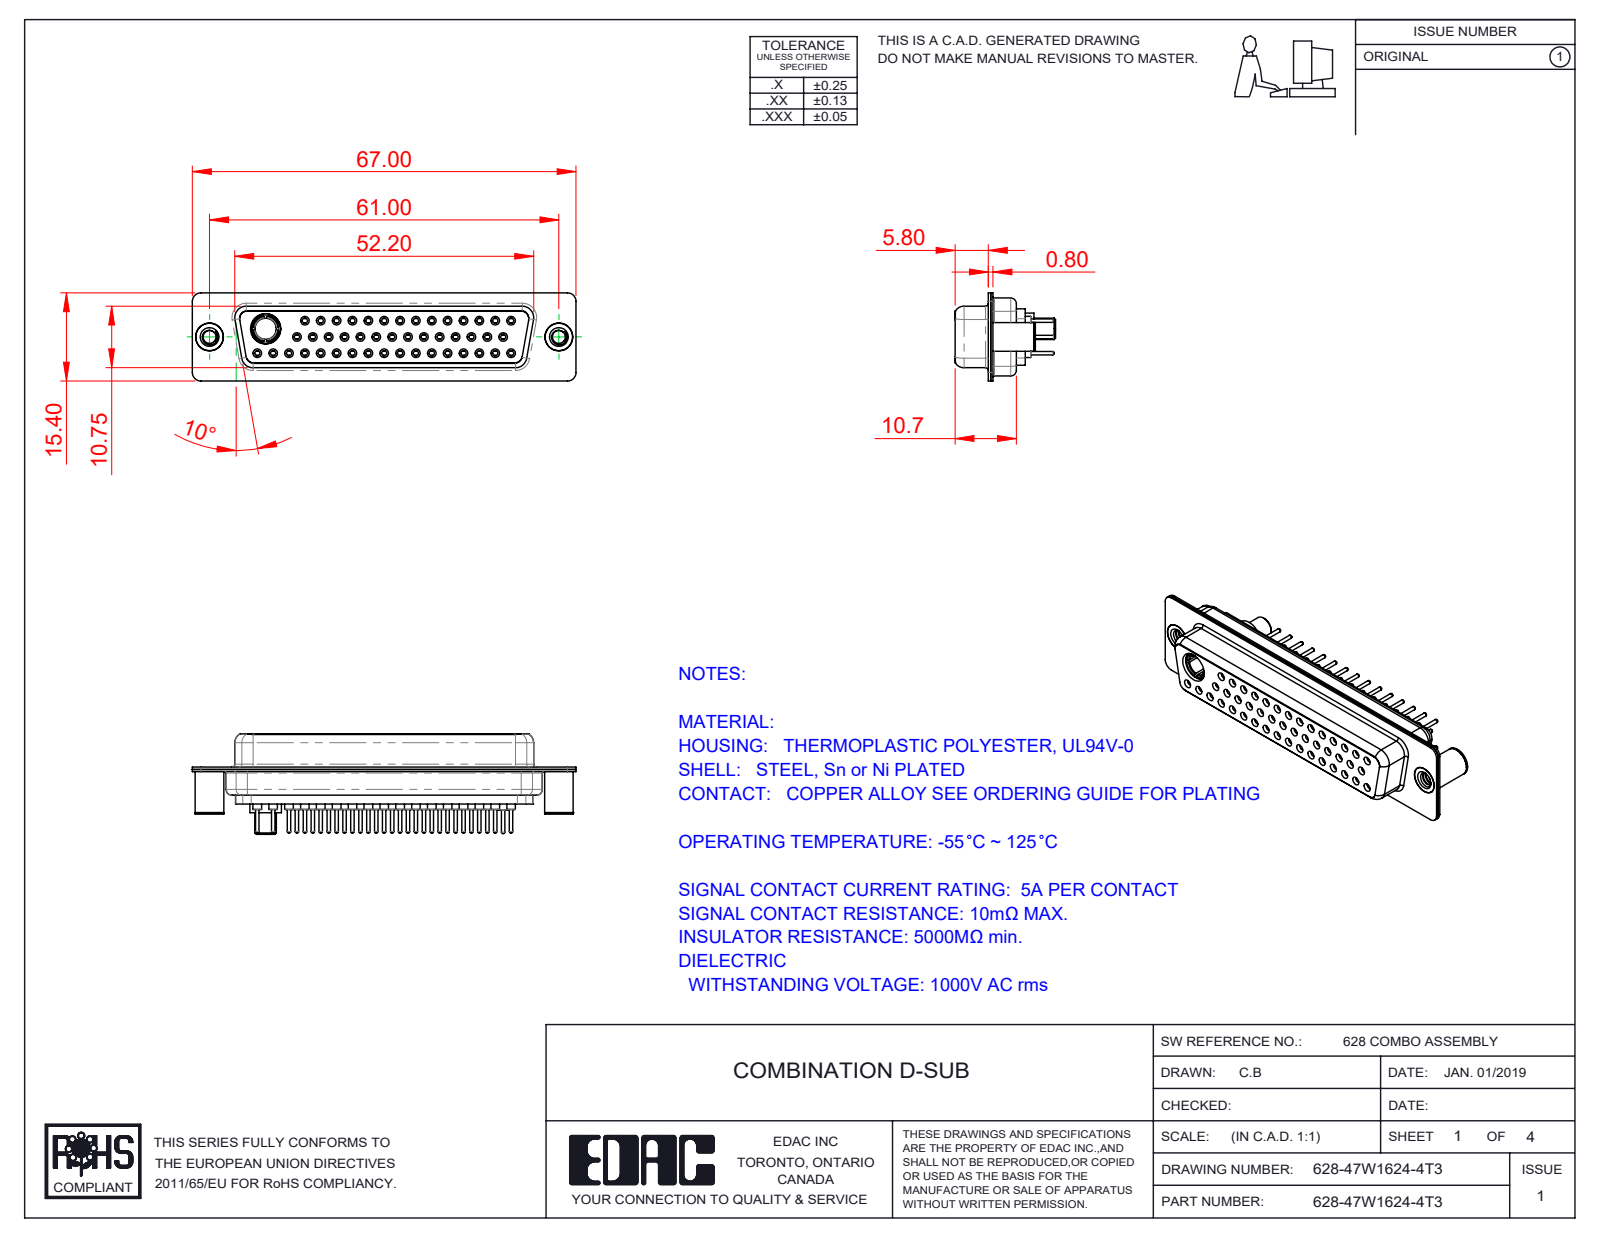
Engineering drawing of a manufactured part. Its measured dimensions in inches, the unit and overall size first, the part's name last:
Units: inches
Overall size (bounding box): 2.638 × 0.691 × 0.606
Round holes (diameter × count): ⌀0.043 ×46, ⌀0.035 ×45, ⌀0.059 ×45, ⌀0.079 ×45, ⌀0.063 ×31, ⌀0.067 ×14, ⌀0.191 ×3, ⌀0.089 ×2, ⌀0.128 ×2, ⌀0.157 ×2, ⌀0.159 ×2, ⌀0.146 ×1
Round bosses / shafts (diameter × count): ⌀0.087 ×46, ⌀0.024 ×46, ⌀0.063 ×15, ⌀0.197 ×2, ⌀0.195 ×2, ⌀0.189 ×2, ⌀0.217 ×1, ⌀0.205 ×1
Partial cylindrical surfaces — rounded edges, fillets, slot ends (radius × count): R0.059 ×16, R0.053 ×12, R0.079 ×12, R0.063 ×8, R0.01 ×4, R0.02 ×4, R0.024 ×4, R0.026 ×4
Main face-to-face distances: 0.016, 0.446, 0.254, 0.238, 0.074, 0.482, 0.244, 0.228, 0.407, 0.43
Hole centre spacings: 0.124, 0.109, 0.218, 0.327, 0.436, 0.545, 0.654, 0.763
Volume: 0.441 in³ · Surface area: 23.19 in²
Bodies: 53 solids, 2905 faces (783 planar, 1050 cylindrical, 1072 other)
Part name (STEP PRODUCT): 628Combo Shell Front_50 Contacts; Power Socket_40A S; 628Combo Threaded Board Spacer_3; 628Combo Shell Rear_50 Contacts (+5 more)
STEP written by: SolidWorks 2016 (CONFIG_CONTROL_DESIGN)
